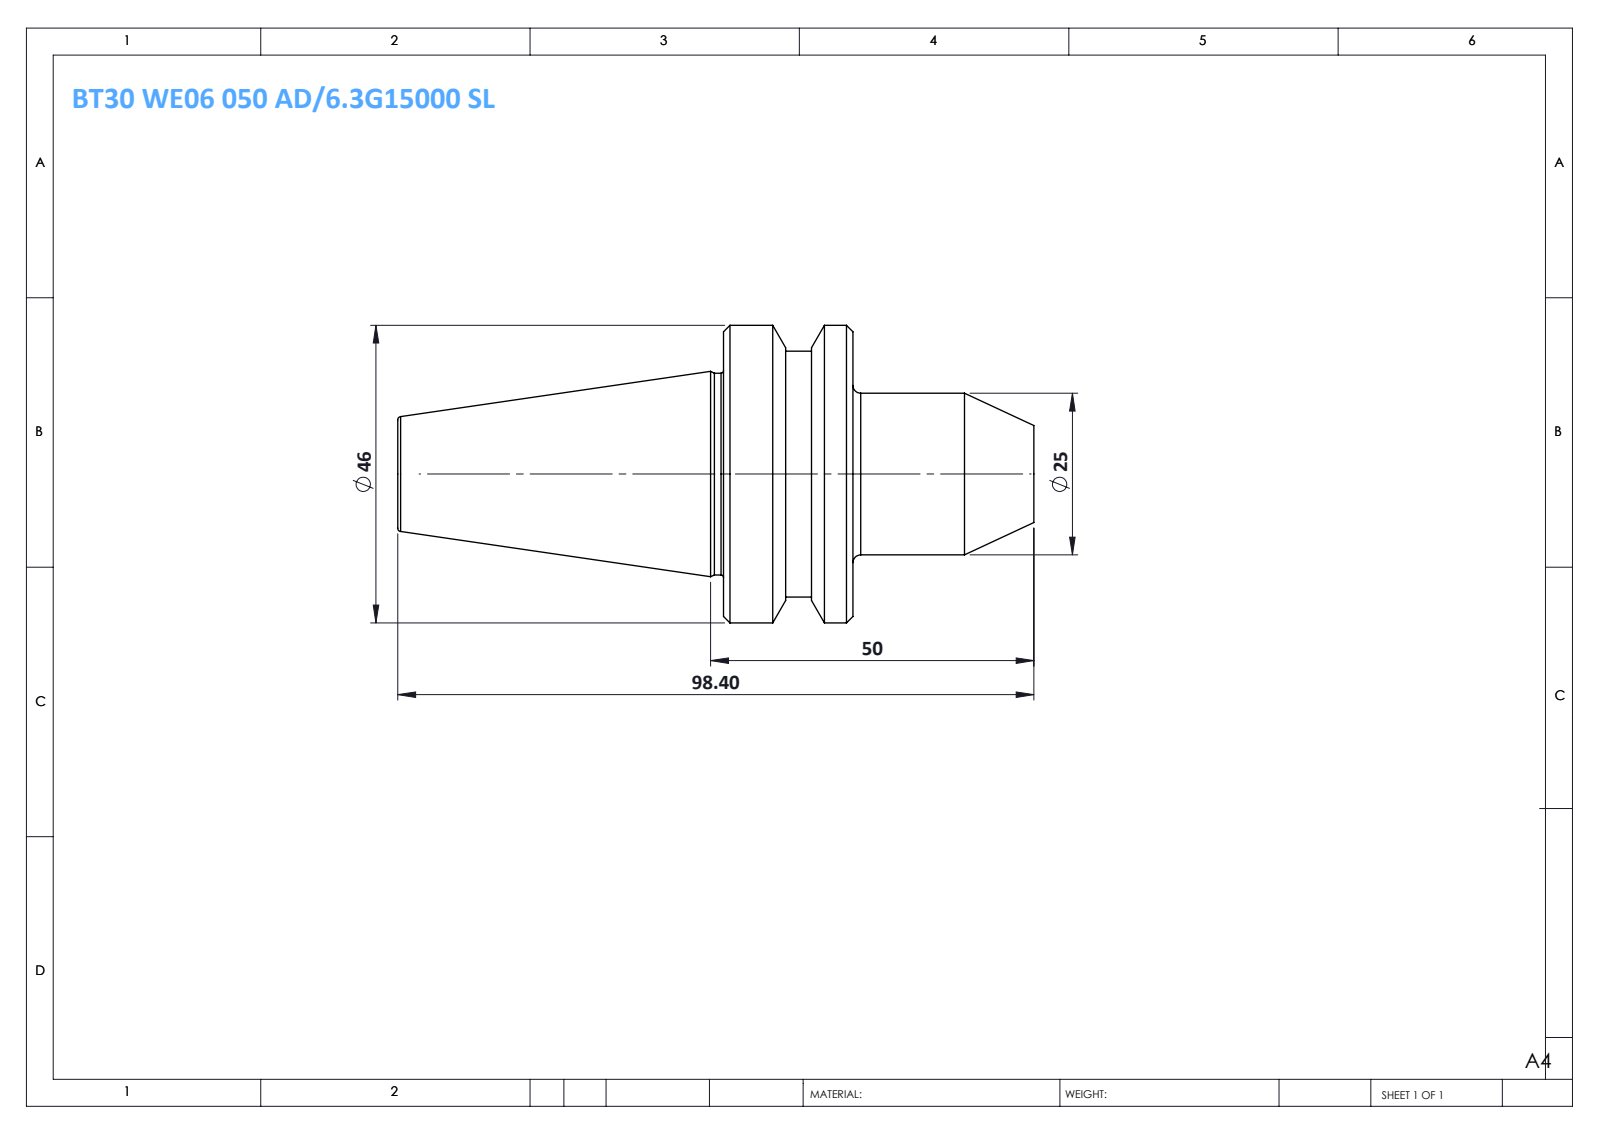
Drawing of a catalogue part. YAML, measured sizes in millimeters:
part_name: "BT30 WE06 050 AD-6.3G15000 SL"
step_written_by: "SolidWorks 2014 (CONFIG_CONTROL_DESIGN)"
units: millimeters
bodies: {solids: 1, faces: 36, planar: 6, cylindrical: 10, other: 20}
overall_size: [98.4, 46, 46]
volume: 67324
surface_area: 11760
round_bosses_or_shafts:
  - {diameter: 46, count: 1}
  - {diameter: 38, count: 1}
  - {diameter: 31.2, count: 1}
  - {diameter: 25, count: 1}
face_to_face_distances: [20, 70.4, 50.4, 28, 48, 98.4, 38.4, 10.4, 9.6, 60]
